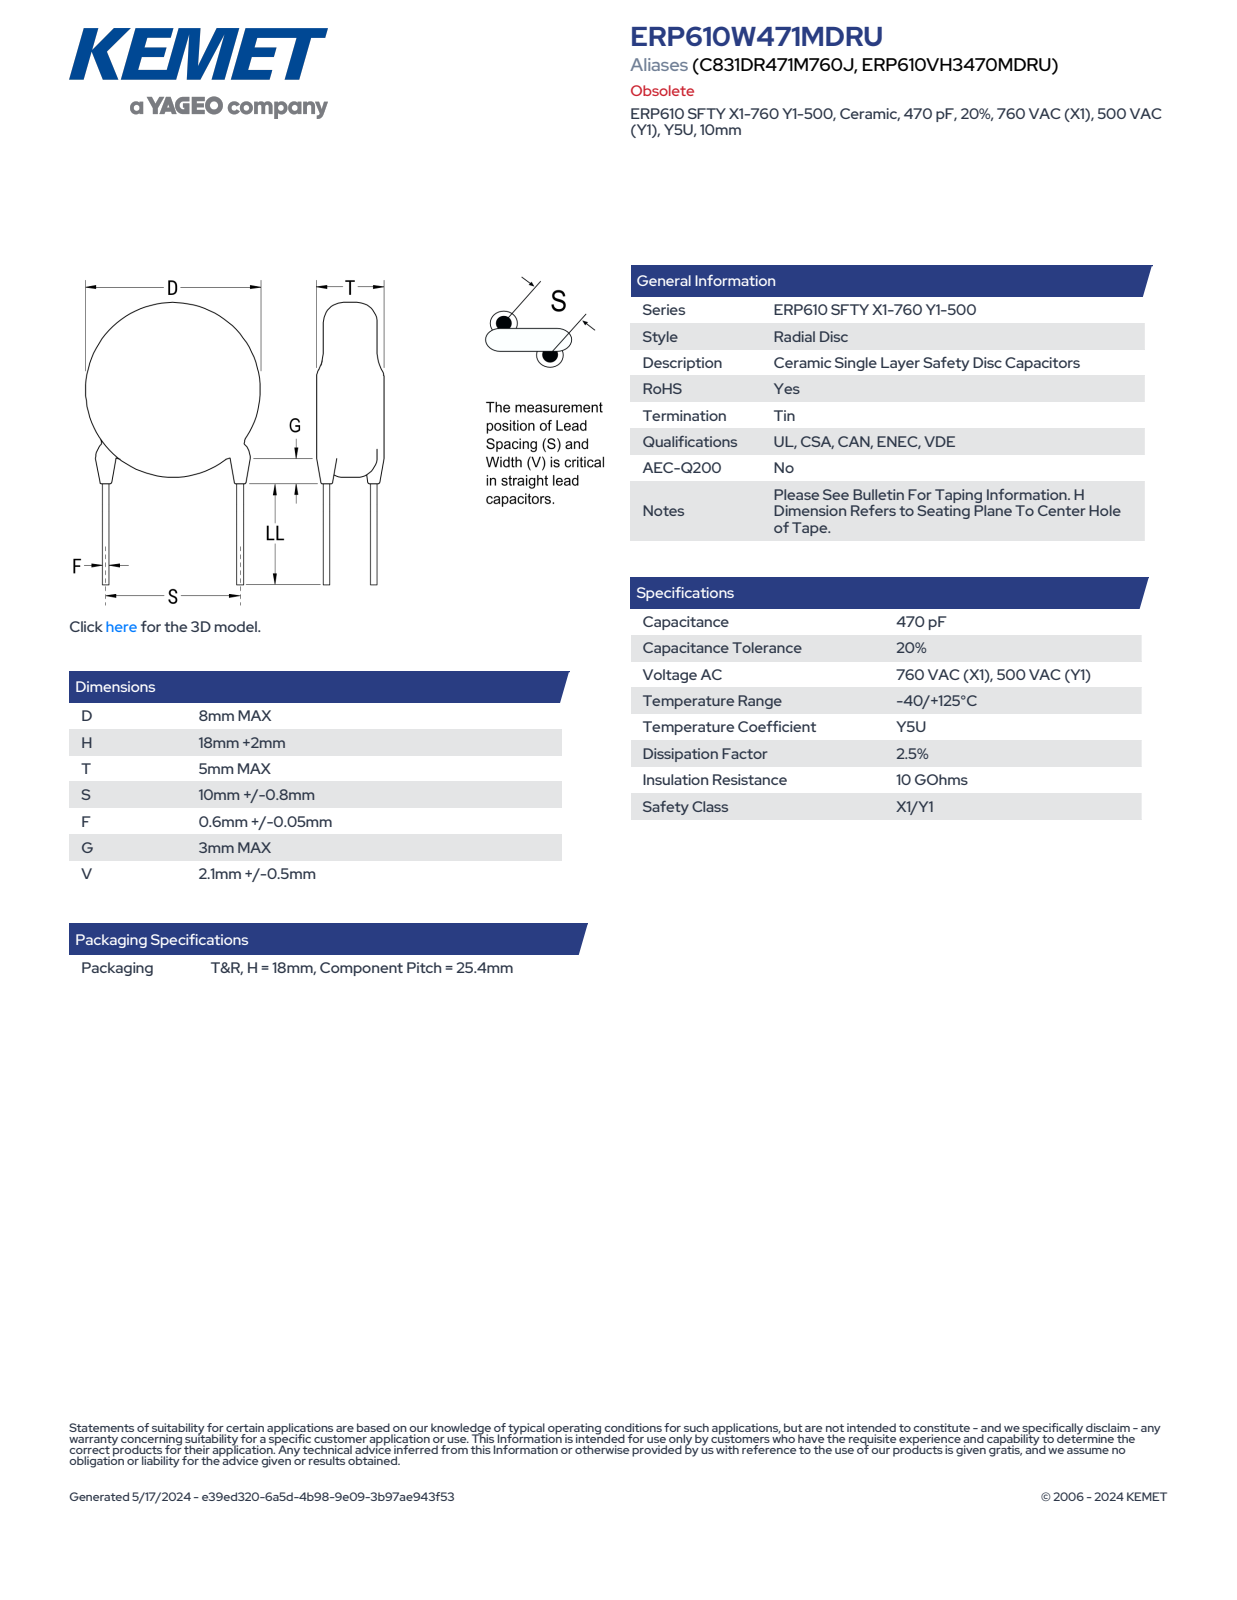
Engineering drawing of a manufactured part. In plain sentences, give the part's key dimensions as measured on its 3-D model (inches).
The part is named "CCD_KST_8X5_D8T5S10LL11F0.65G3V2.6". Its 3-D file was written by "SolidWorks 2014 (AUTOMOTIVE_DESIGN)". It is 4 solids with 81 faces: 63 planar, 6 cylindrical and 12 other. Overall it measures 0.757 by 0.406 by 0.197 inches. Its volume is 0.015 cubic inches and its surface area 0.415 square inches. Round bosses or shafts: 2 of diameter 0.026, 1 of diameter 0.315. The main face-to-face distances are 0.197, 0.039, 0.619, 0.58, 0.044, 0.16, 0.032, 0.024, 0.014, 0.116.
